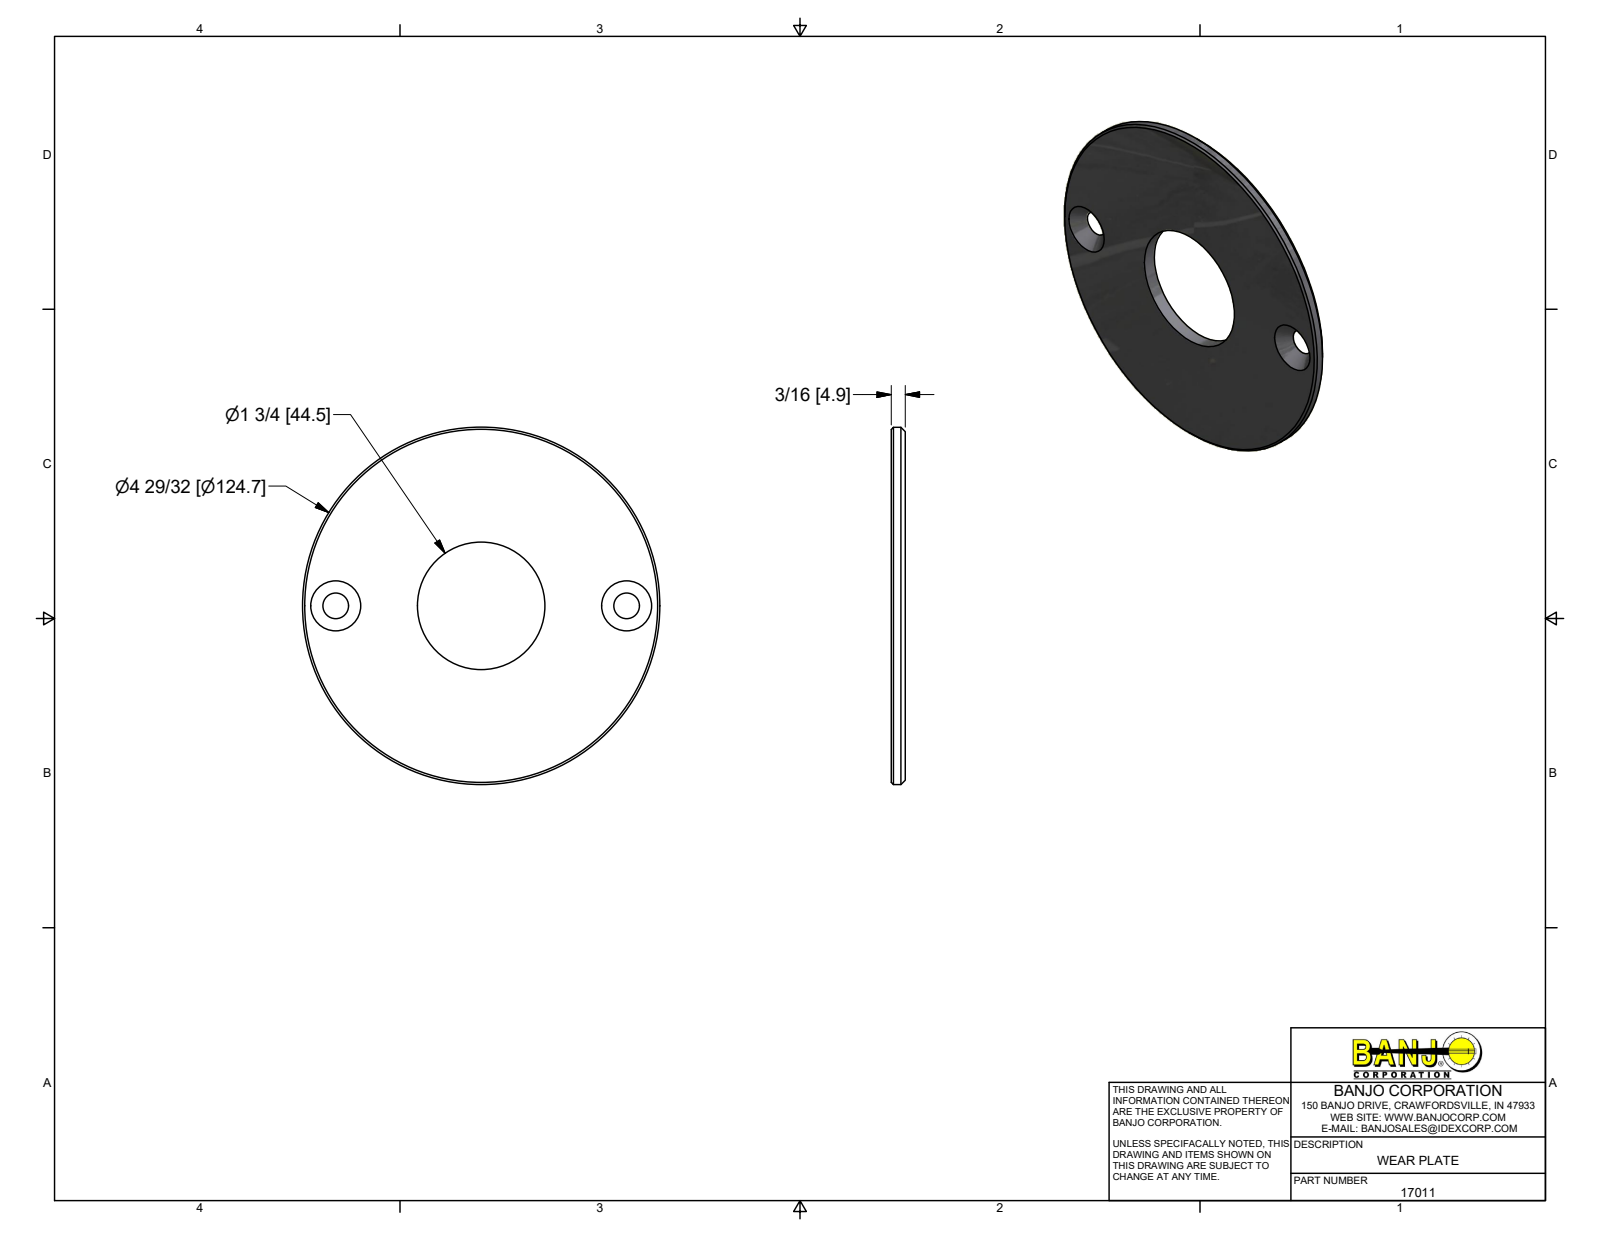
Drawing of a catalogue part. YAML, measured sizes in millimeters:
part_name: "17011"
step_written_by: "Autodesk Inventor 2017 (AUTOMOTIVE_DESIGN)"
units: millimeters
bodies: {solids: 1, faces: 8, planar: 2, cylindrical: 2, other: 4}
overall_size: [124.71, 124.71, 4.9]
volume: 50324
surface_area: 23339
round_holes:
  - {diameter: 44.45, count: 1}
round_bosses_or_shafts:
  - {diameter: 124.71, count: 1}
face_to_face_distances: [4.9]
